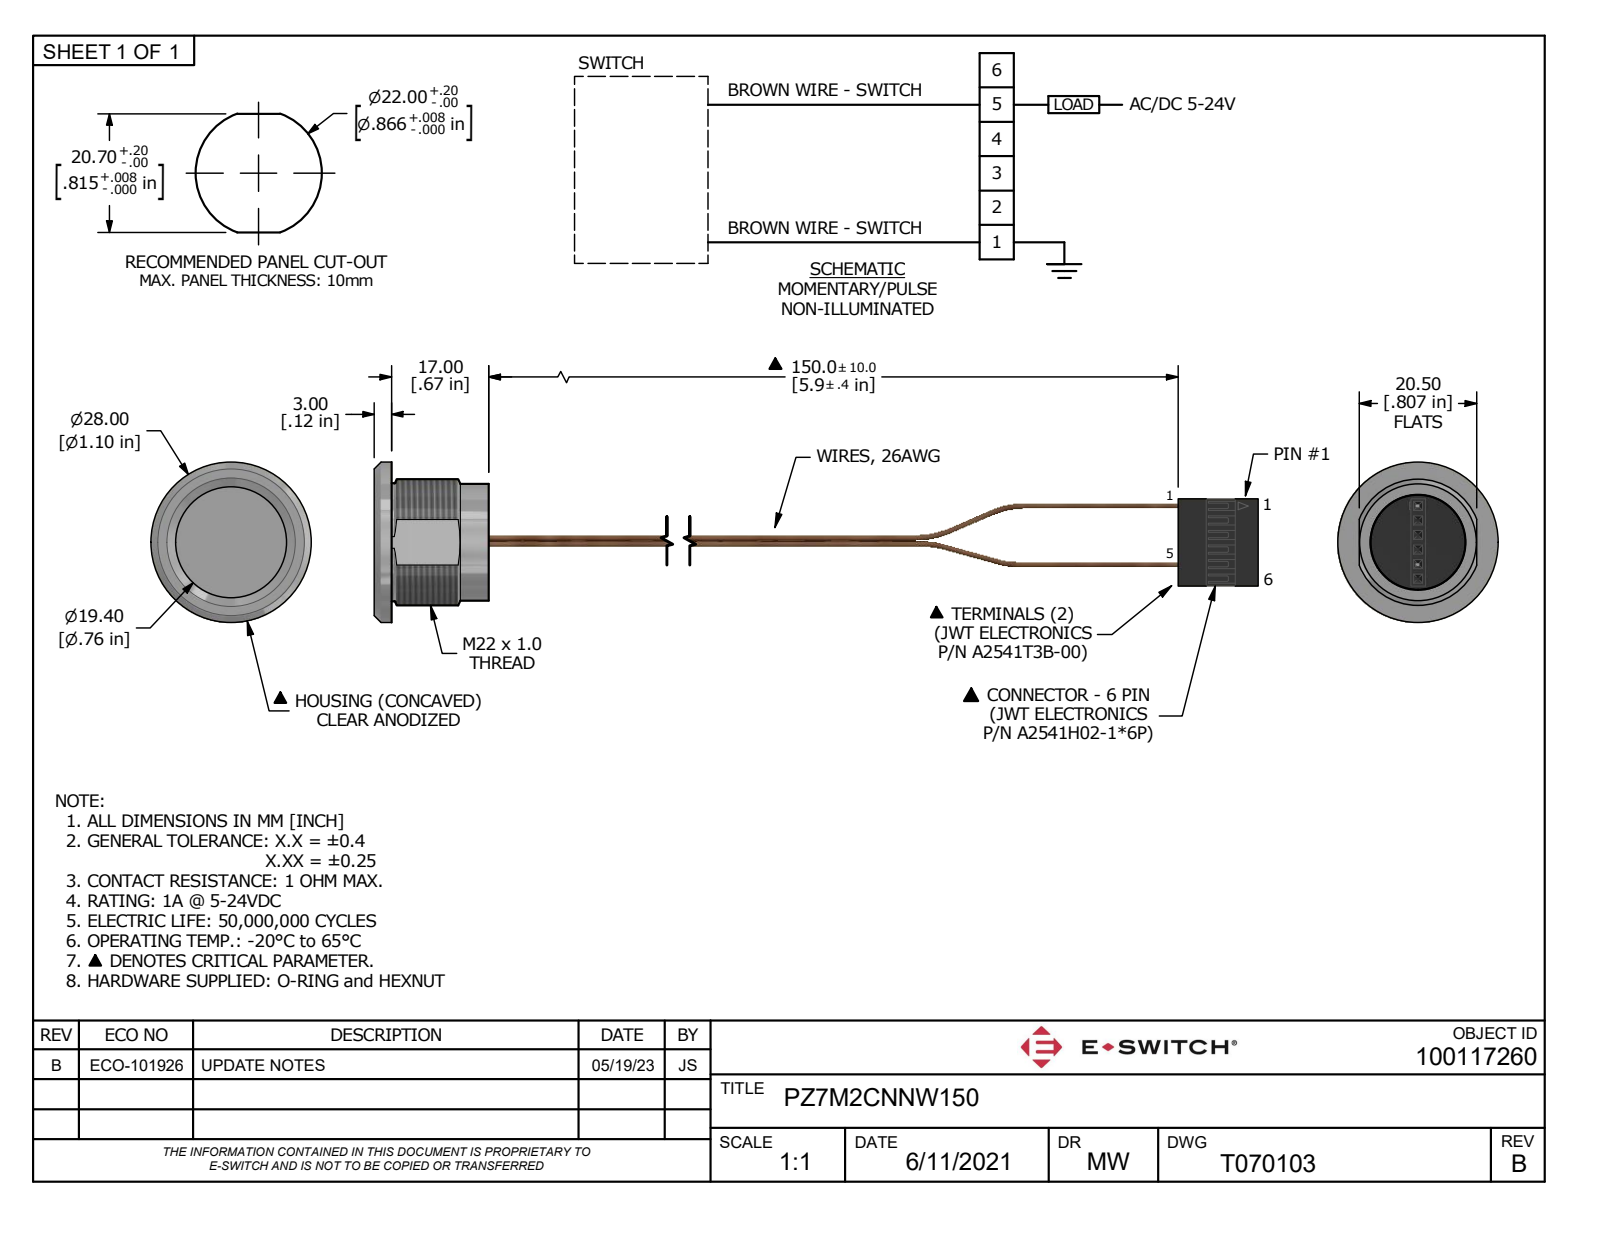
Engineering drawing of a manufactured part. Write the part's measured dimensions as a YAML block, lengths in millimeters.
part_name: "PZ7M2CNNW150"
step_written_by: "Autodesk Inventor 2020 (AUTOMOTIVE_DESIGN)"
units: millimeters
bodies: {solids: 4, faces: 166, planar: 128, cylindrical: 26, other: 12}
overall_size: [184, 28, 28]
volume: 8077
surface_area: 4612
round_bosses_or_shafts:
  - {diameter: 1, count: 6}
  - {diameter: 0.7, count: 2}
  - {diameter: 28, count: 1}
  - {diameter: 20.6, count: 1}
  - {diameter: 20.4, count: 1}
partial_cylinders:
  - {radius: 0.25, count: 12}
  - {radius: 11, count: 1}
face_to_face_distances: [2.54, 2, 0.47, 2.07, 8.98, 11.52, 1.6, 11.05, 9.45, 5.08]
